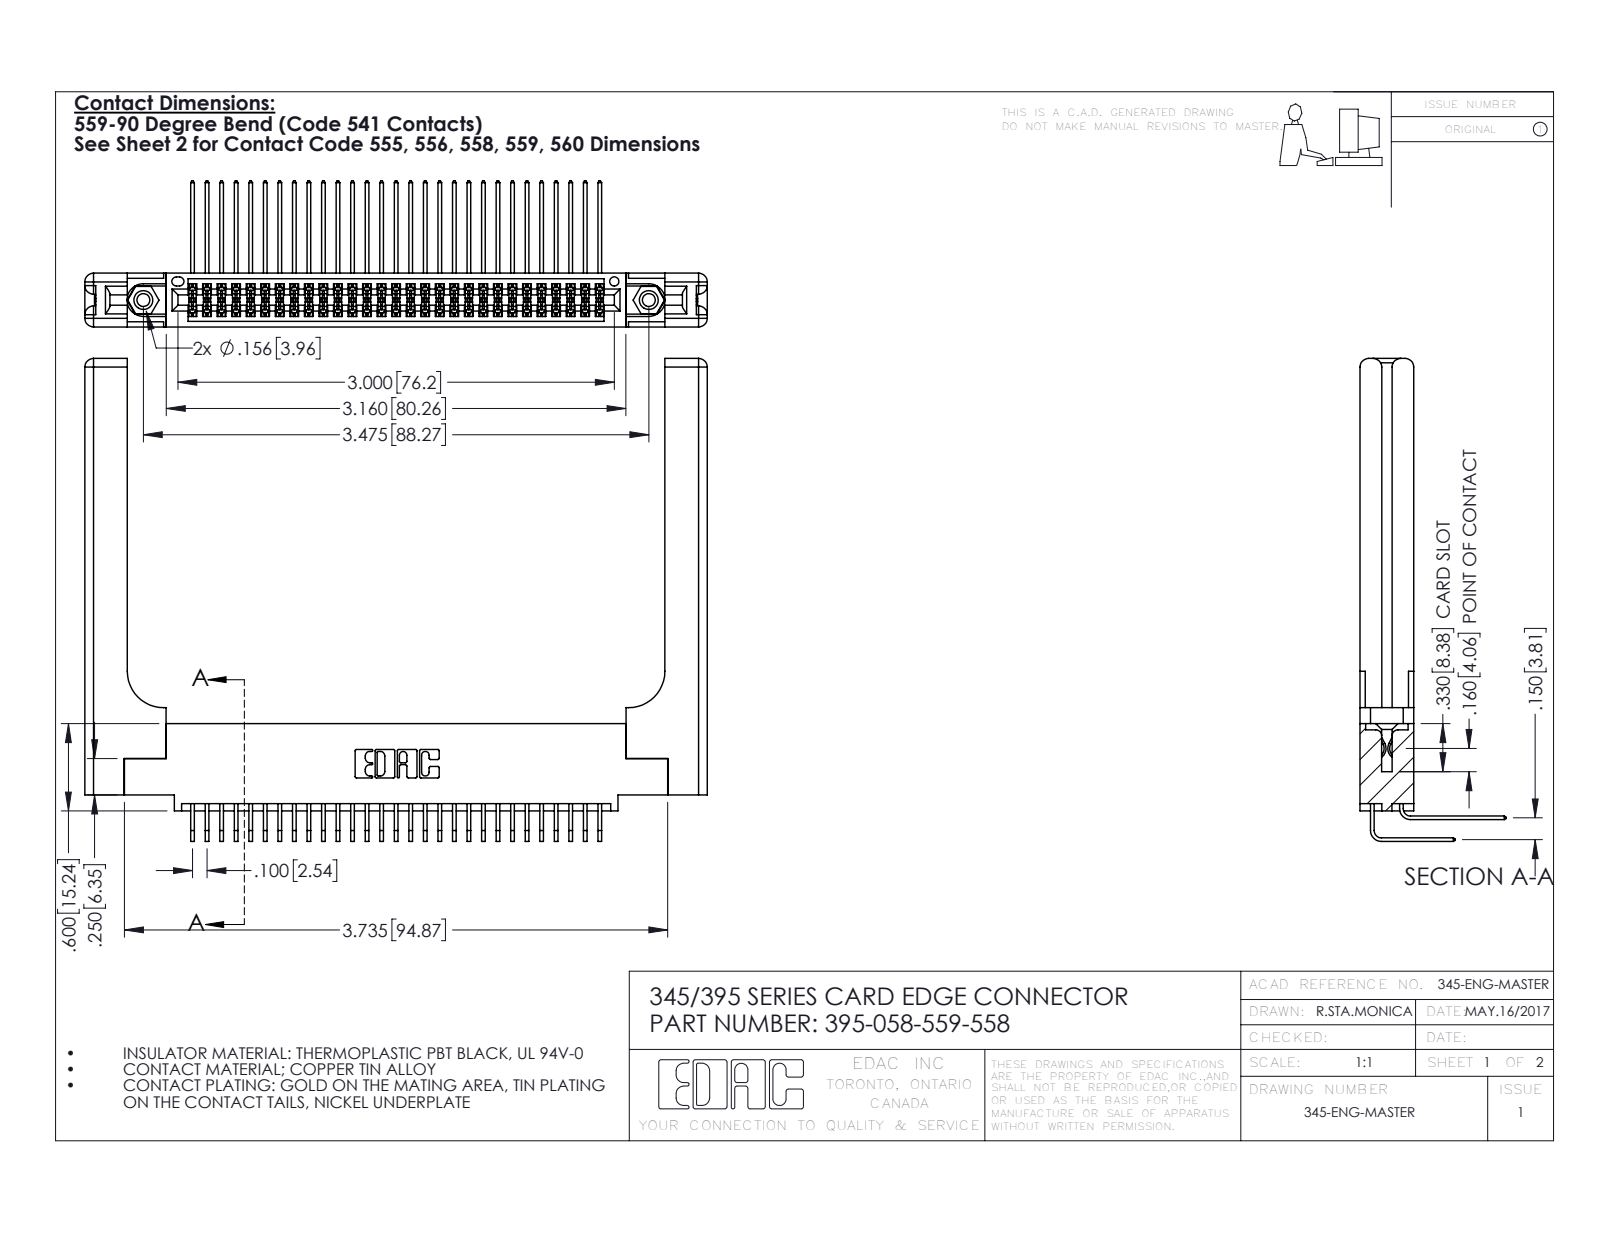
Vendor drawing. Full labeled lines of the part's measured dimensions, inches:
Part name (STEP PRODUCT): 345 Part_0.110 Offset - 0.156 Dia-TH; 345-292-001_558 559 Tail - 1; 345-250-001_345-250-001-102; 345-292-001_559 Tail - 2 (+2 more)
STEP written by: SolidWorks 2016 (CONFIG_CONTROL_DESIGN)
Units: inches
Bodies: 63 solids, 3402 faces (2262 planar, 1080 cylindrical, 60 other)
Overall size (bounding box): 4.279 × 3.319 × 1.005
Volume: 1.17 in³ · Surface area: 34.55 in²
Round holes (diameter × count): ⌀0.089 ×2, ⌀0.125 ×2, ⌀0.156 ×2, ⌀0.064 ×1
Round bosses / shafts (diameter × count): ⌀0.155 ×2
Partial cylindrical surfaces — rounded edges, fillets, slot ends (radius × count): R0.006 ×88, R0.01 ×22, R0.06 ×16, R0.007 ×6, R0.031 ×6, R0.026 ×3, R0.014 ×2, R0.019 ×2
Main face-to-face distances: 0.37, 0.072, 0.298, 0.098, 0.272, 0.025, 0.2, 0.225, 0.148, 0.15
Hole centre spacings: 0.27, 3.24, 3.475
